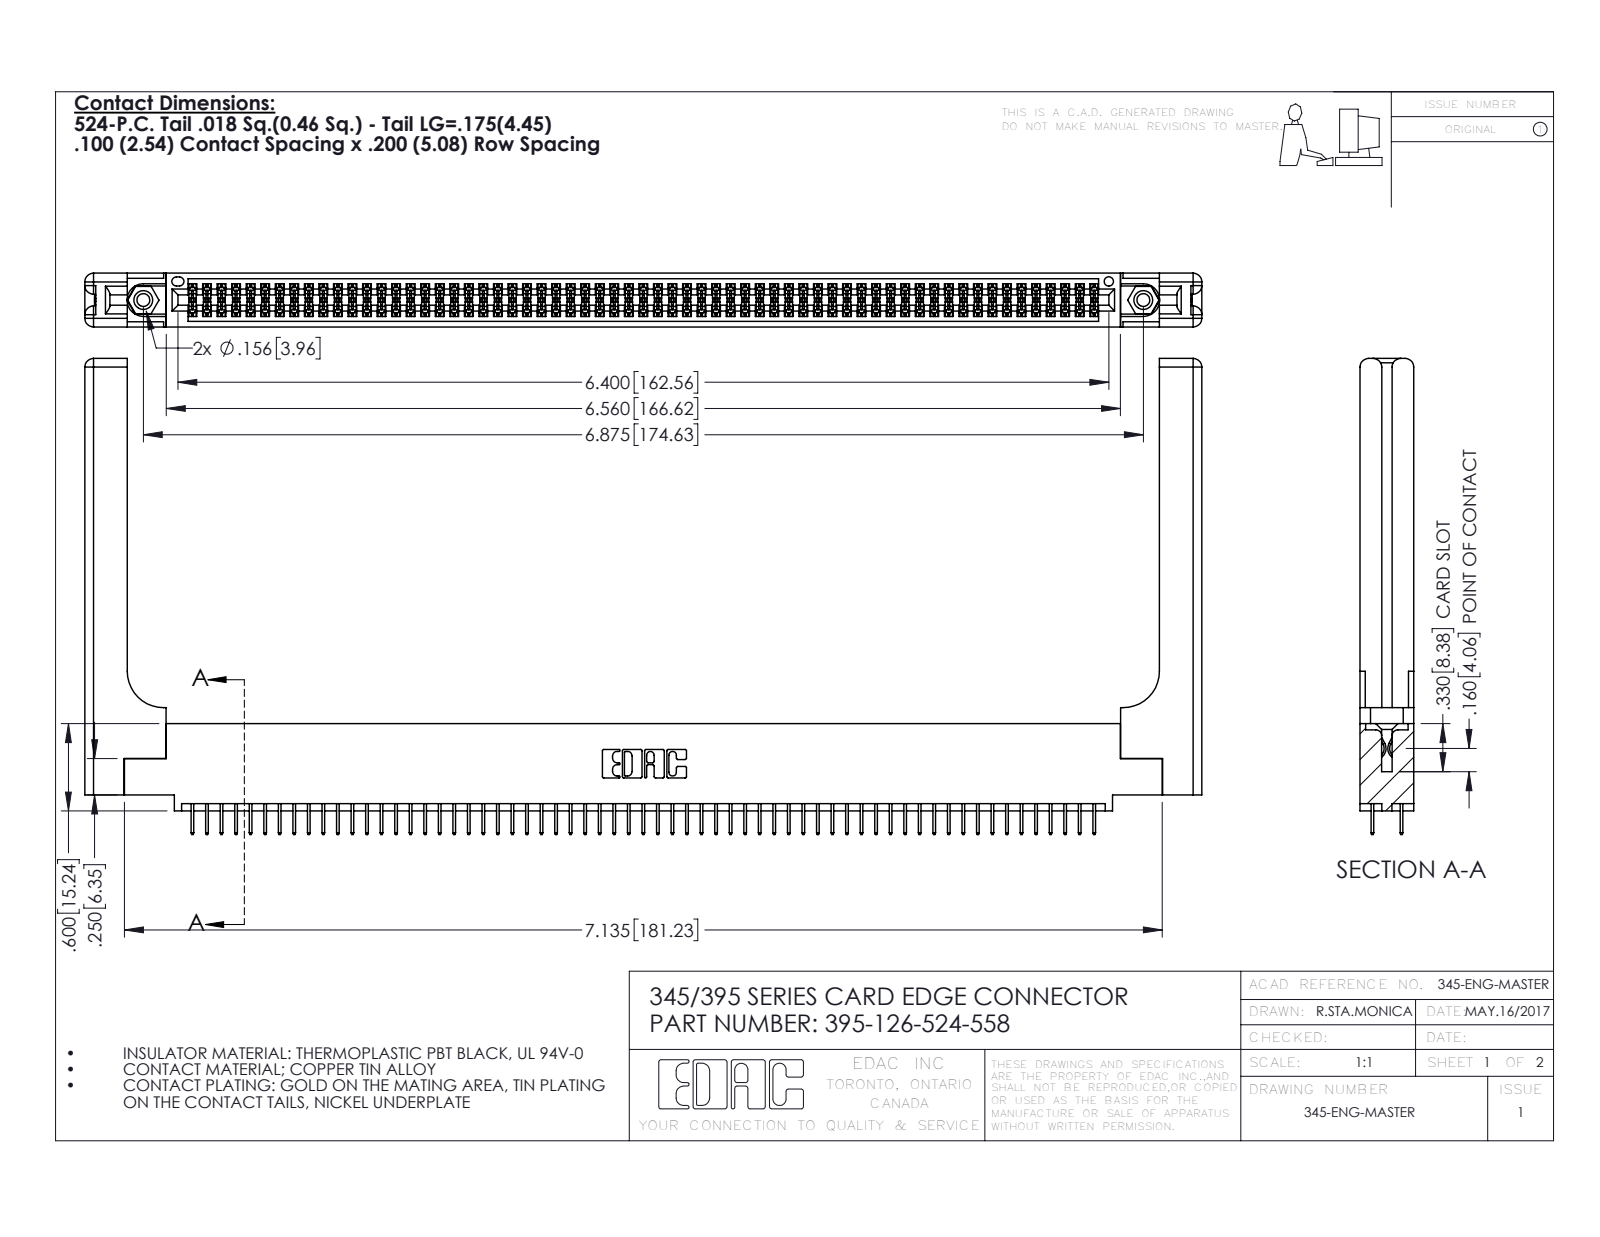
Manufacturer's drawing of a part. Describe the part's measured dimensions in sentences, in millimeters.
The part is named "345-250-001_345-250-001-102; 345-292-001_345-293-124; 345-220-058_345-220-058; 395-126-524-558 (+1 more)". Its 3-D file was written by "SolidWorks 2016 (CONFIG_CONTROL_DESIGN)". It is 131 solids with 7190 faces: 5146 planar, 1984 cylindrical and 60 other. Overall it measures 195 by 83.1 by 9.4 millimeters. Its volume is 27 350 cubic millimeters and its surface area 32 960 square millimeters. Round holes: 2 of diameter 2.3, 2 of diameter 3.2, 2 of diameter 4, 1 of diameter 1.6. Round bosses or shafts: 2 of diameter 3.9. Partial cylindrical surfaces (rounded edges, fillets, slot ends): 189 of radius 0.2, 22 of radius 0.3, 16 of radius 1.5, 6 of radius 0.2, 6 of radius 0.8, 3 of radius 0.7, 2 of radius 0.4, 2 of radius 0.5. The main face-to-face distances are 1.8, 7.6, 9.4, 5.1, 2.5, 6.9, 0.6, 5.7, 1.8, 3.8. The hole center spacings are 6.9, 168.6, 174.6.
